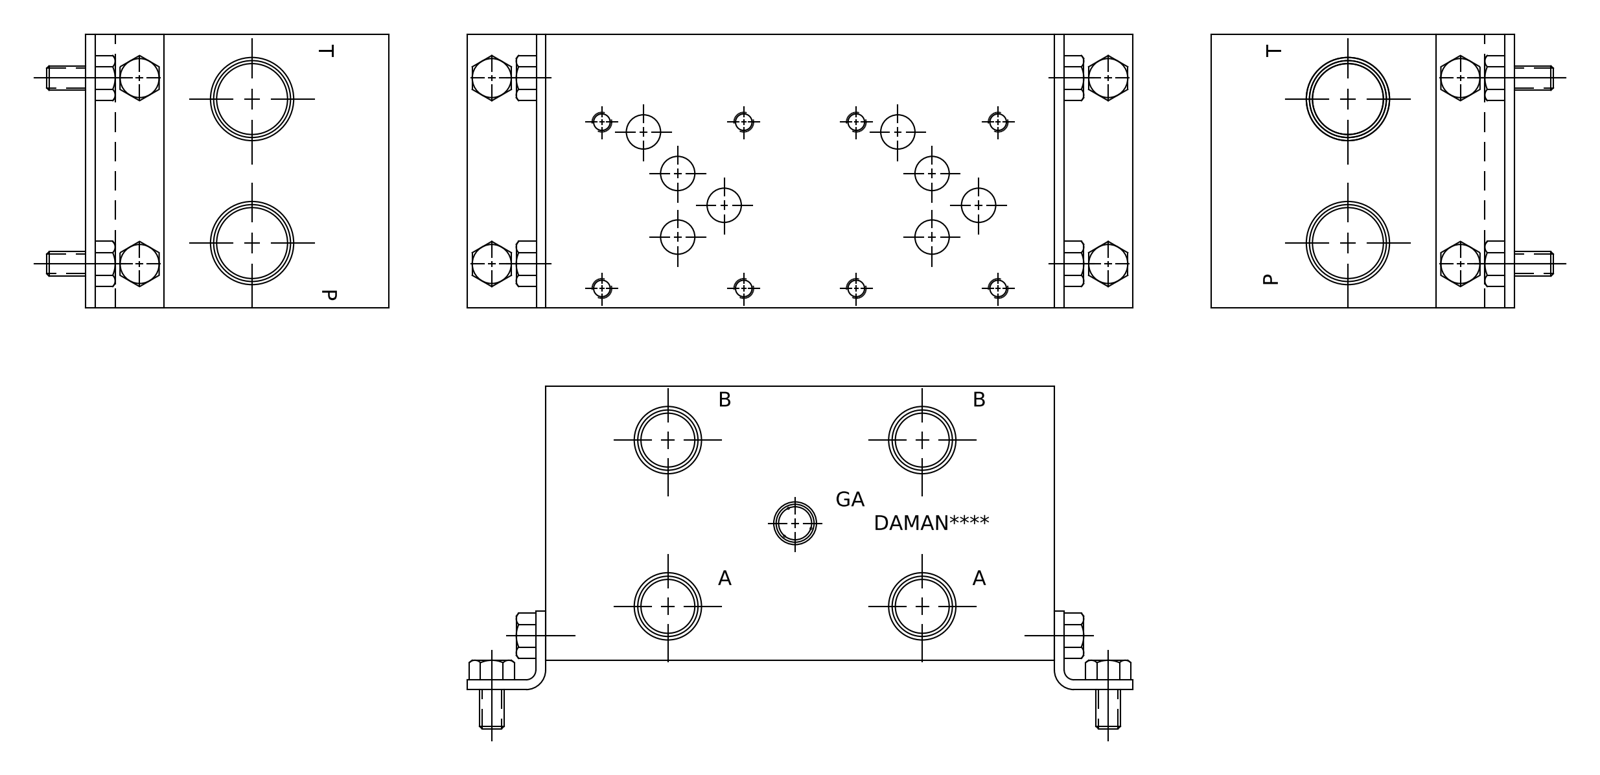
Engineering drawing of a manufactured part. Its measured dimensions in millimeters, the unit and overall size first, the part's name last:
Units: millimetres
Overall size (bounding box): 165.1 × 88.9 × 88.9
Round holes (diameter × count): ⌀5.11 ×8, ⌀6.35 ×8, ⌀11.13 ×7, ⌀17.48 ×4, ⌀21.59 ×4, ⌀6.53 ×2, ⌀7.92 ×2, ⌀23.01 ×2, ⌀26.92 ×2, ⌀10.72 ×1, ⌀11.11 ×1, ⌀13.87 ×1
Main face-to-face distances: 88.9, 165.1, 15.85, 149.25, 15.37, 73.53, 133.4, 1, 14.37, 87.9
Hole centre spacings: 82.55, 46.05, 70.95, 53.98, 98.63, 13.88, 18.27, 27.13
Volume: 1 226 000 mm³ · Surface area: 92 057 mm²
Bodies: 1 solid, 584 faces (348 planar, 50 cylindrical, 186 other)
Part name (STEP PRODUCT): Part_AD05P023P_3D
STEP written by: Autodesk Inventor 2019 (AUTOMOTIVE_DESIGN)
